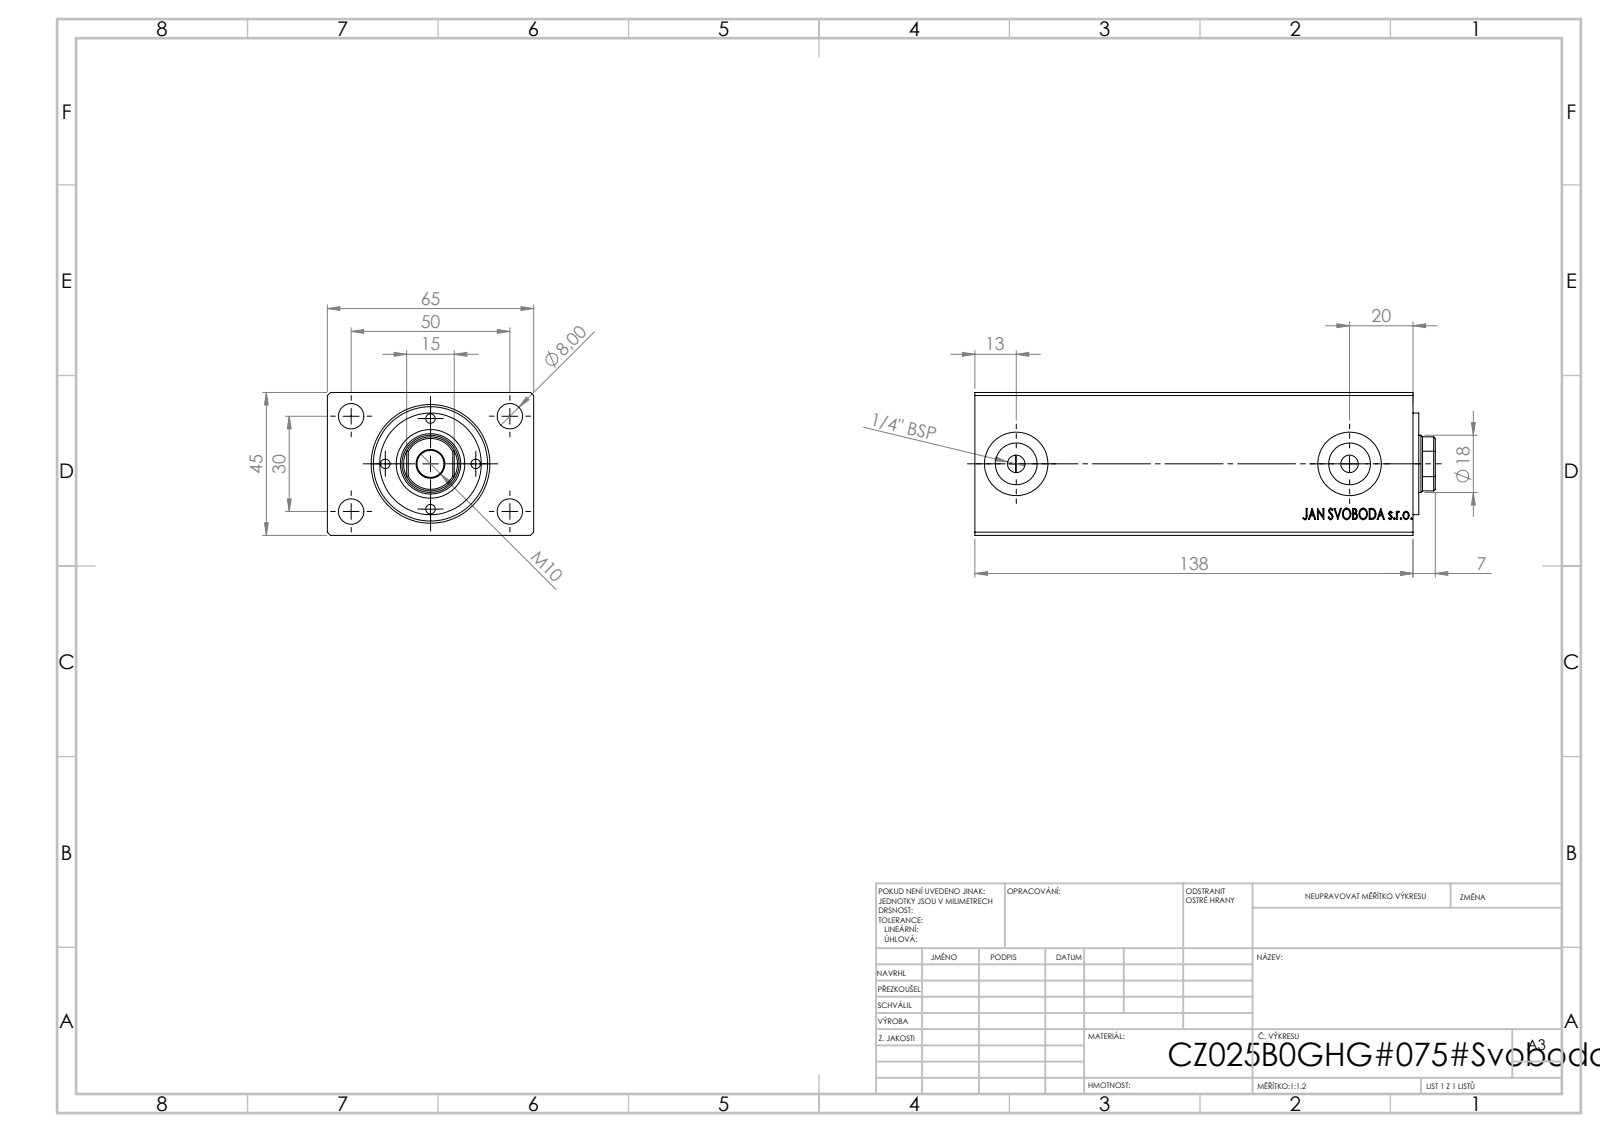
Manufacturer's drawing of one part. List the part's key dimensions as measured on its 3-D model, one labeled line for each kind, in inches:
Part name (STEP PRODUCT): V500CZ_B_VC; V500CZ
STEP written by: SolidWorks 2019 (CONFIG_CONTROL_DESIGN)
Units: inches
Bodies: 3 solids, 873 faces (399 planar, 58 cylindrical, 416 other)
Overall size (bounding box): 5.709 × 2.559 × 1.772
Volume: 22.66 in³ · Surface area: 100.5 in²
Round holes (diameter × count): ⌀0.118 ×4, ⌀0.315 ×4, ⌀0.217 ×2, ⌀0.518 ×2, ⌀0.787 ×2, ⌀0.335 ×1, ⌀0.709 ×1, ⌀0.748 ×1, ⌀0.984 ×1, ⌀1.417 ×1
Round bosses / shafts (diameter × count): ⌀1.26 ×1
Partial cylindrical surfaces — rounded edges, fillets, slot ends (radius × count): R0.335 ×1
Main face-to-face distances: 1.772, 2.559, 5.433, 0.276, 5.425, 4.929, 0.496, 0.504, 0.071, 0.205
Hole centre spacings: 0.561, 0.726, 0.793, 0.985, 1.148, 1.515, 1.654, 1.122
